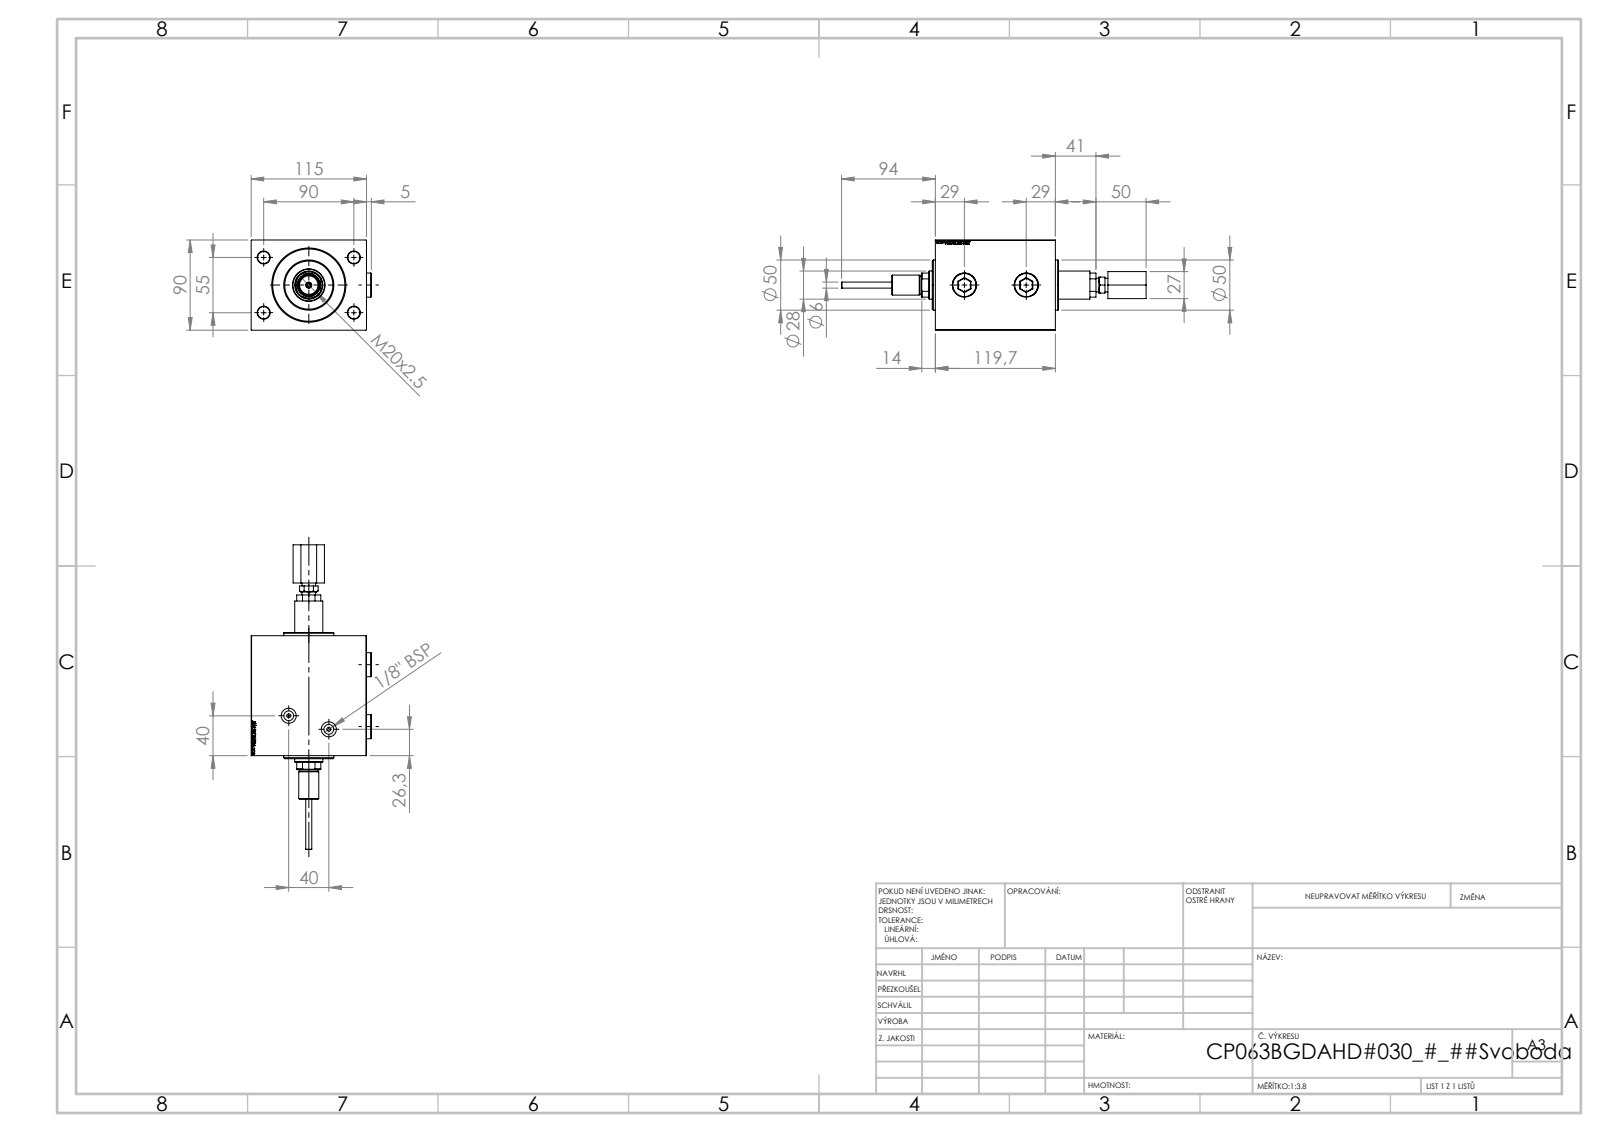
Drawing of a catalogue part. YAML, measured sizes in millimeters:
part_name: "V450DCP_B_Body; PLUG; V450DCP_VC_B; V450CP_MALE_METRIC (+2 more)"
step_written_by: "SolidWorks 2019 (CONFIG_CONTROL_DESIGN)"
units: millimeters
bodies: {solids: 7, faces: 1040, planar: 472, cylindrical: 114, other: 454}
overall_size: [303.7, 119.9, 90]
volume: 1201000
surface_area: 166444
round_holes:
  - {diameter: 6, count: 4}
  - {diameter: 12, count: 4}
  - {diameter: 16.17, count: 3}
  - {diameter: 24, count: 3}
  - {diameter: 4, count: 2}
  - {diameter: 9.73, count: 2}
  - {diameter: 15, count: 2}
  - {diameter: 3, count: 1}
  - {diameter: 18.5, count: 1}
  - {diameter: 28, count: 1}
  - {diameter: 31.5, count: 1}
  - {diameter: 32.5, count: 1}
round_bosses_or_shafts:
  - {diameter: 50, count: 1}
  - {diameter: 20, count: 1}
  - {diameter: 18, count: 1}
  - {diameter: 13.47, count: 1}
partial_cylinders:
  - {radius: 13.5, count: 1}
face_to_face_distances: [90, 115, 119.7, 17.5, 102.2, 30, 77.5, 60, 42.2, 1]
hole_center_spacings: [52.74, 55, 90, 105.48, 7.5, 42.22, 61.7, 69.2]
